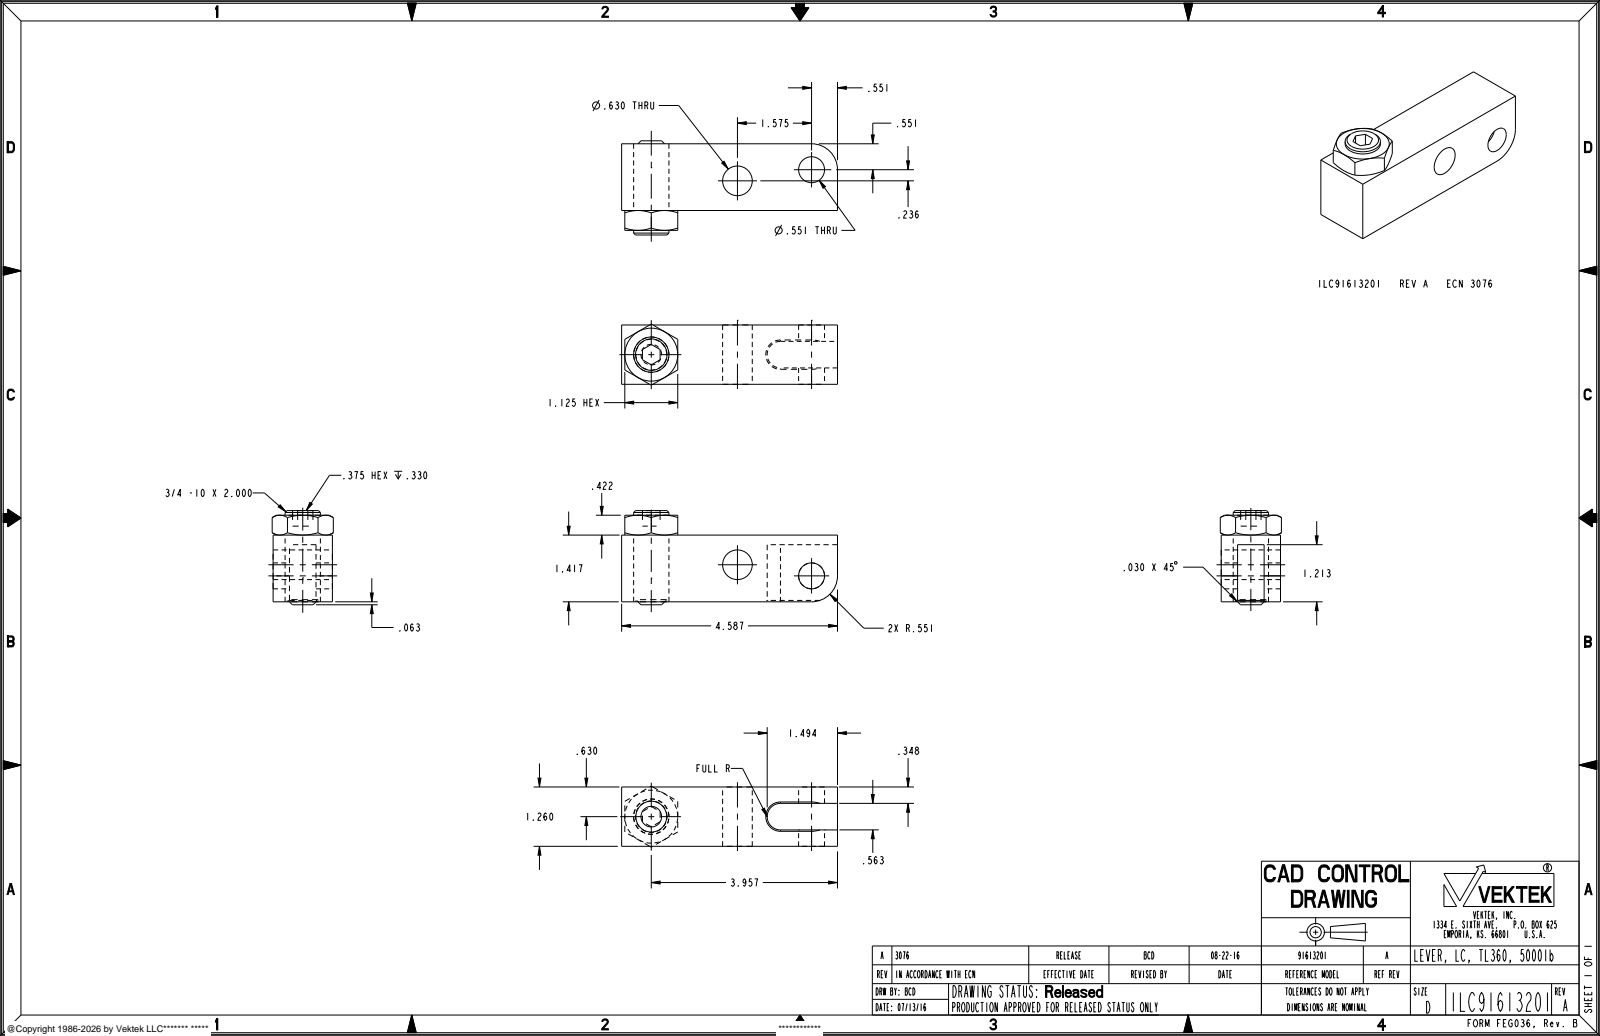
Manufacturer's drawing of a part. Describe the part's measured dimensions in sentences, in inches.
The part is named "ILC91613201". Its 3-D file was written by "PRO/ENGINEER BY PARAMETRIC TECHNOLOGY CORPORATION, 2013320 (AUTOMOTIVE_DESIGN)". It is 1 solid with 59 faces: 27 planar, 15 cylindrical and 17 other. Overall it measures 4.587 by 2 by 1.299 inches. Its volume is 7.075 cubic inches and its surface area 38.97 square inches. Round holes: 1 of diameter 0.551, 1 of diameter 0.63, 1 of diameter 0.656. Round bosses or shafts: 1 of diameter 0.75. Partial cylindrical surfaces (rounded edges, fillets, slot ends): 1 of radius 0.282, 1 of radius 0.551. The main face-to-face distances are 1.26, 1.417, 0.348, 0.912, 0.564, 1.213, 0.204, 4.587, 1.839, 0.626. The hole center spacings are 1.593.
